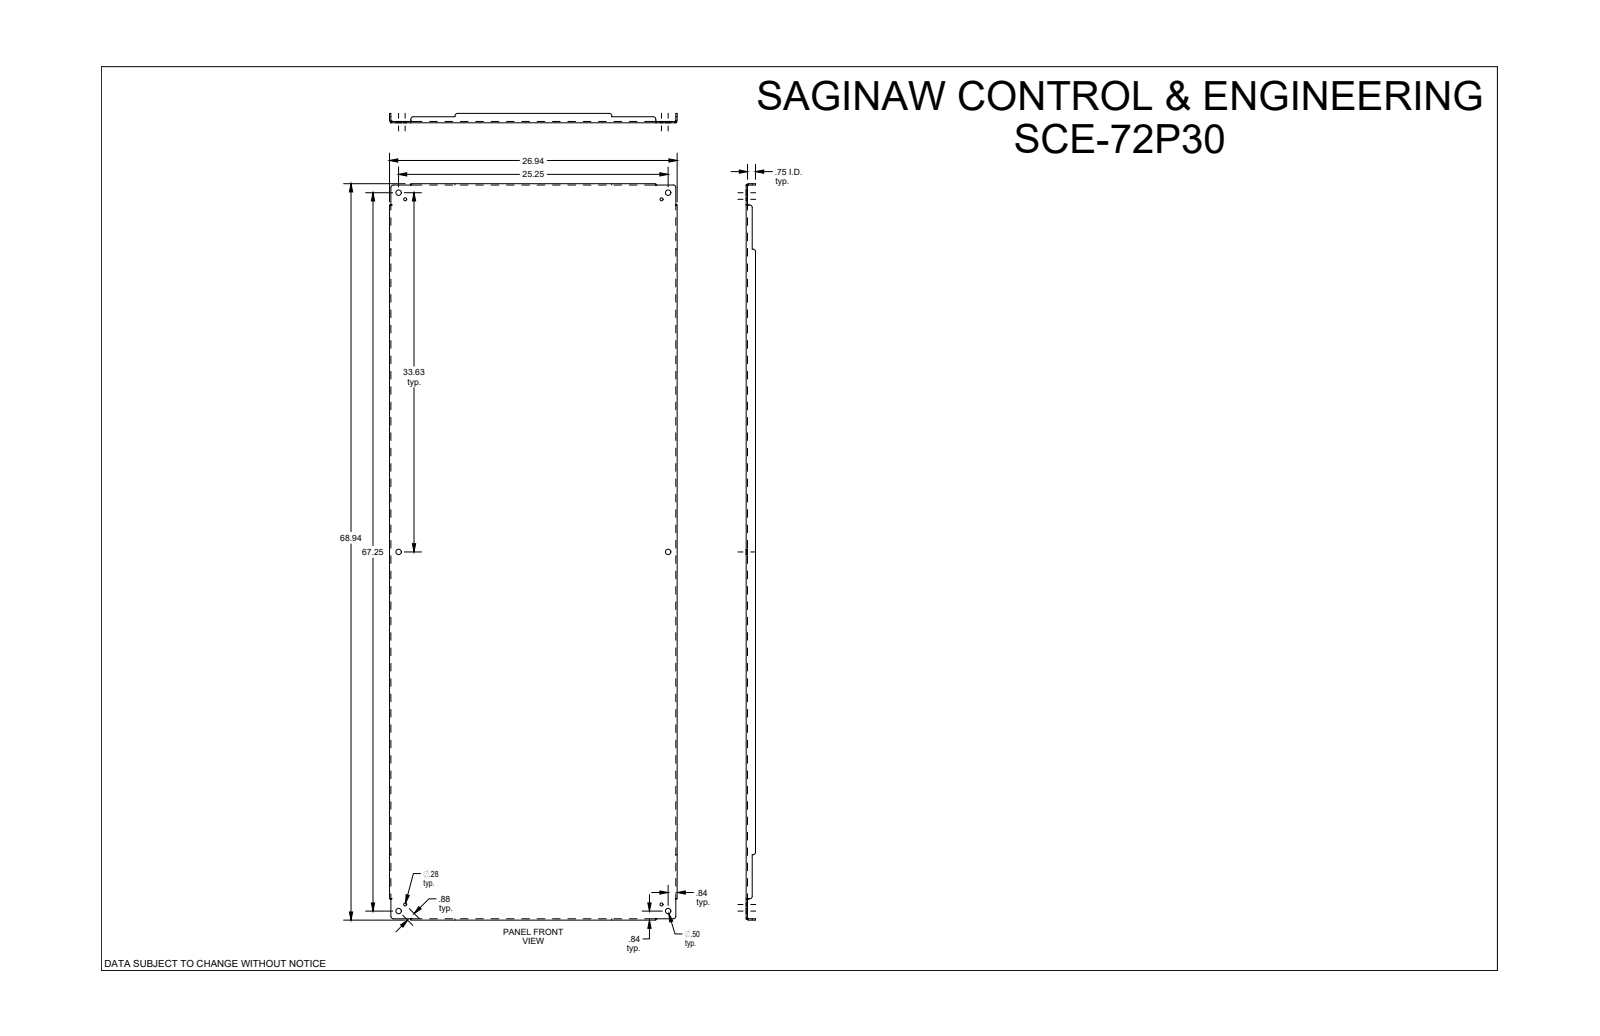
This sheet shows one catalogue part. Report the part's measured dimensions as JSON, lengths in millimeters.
{"part_name": "SCE-72P30", "step_written_by": "SolidWorks 2019 (CONFIG_CONTROL_DESIGN)", "units": "millimeters", "bodies": {"solids": 1, "faces": 108, "planar": 46, "cylindrical": 38, "other": 24}, "overall_size": [1751, 684.2, 22.2], "volume_mm3": 4018000, "surface_area_mm2": 2548000, "round_holes": [[12.7, 6], [7.1, 4]], "partial_cylinders_radius": [[6.4, 12], [2.8, 4], [6, 4]], "face_to_face_distances": [3.2, 3.2, 681.1, 677.8, 684.2, 1747.9, 19.1, 22.2, 1744.6, 1751], "hole_center_spacings": [22.2, 625.8, 838.5, 854.1, 1046.1, 1068.1, 1692.5, 1804.4]}
